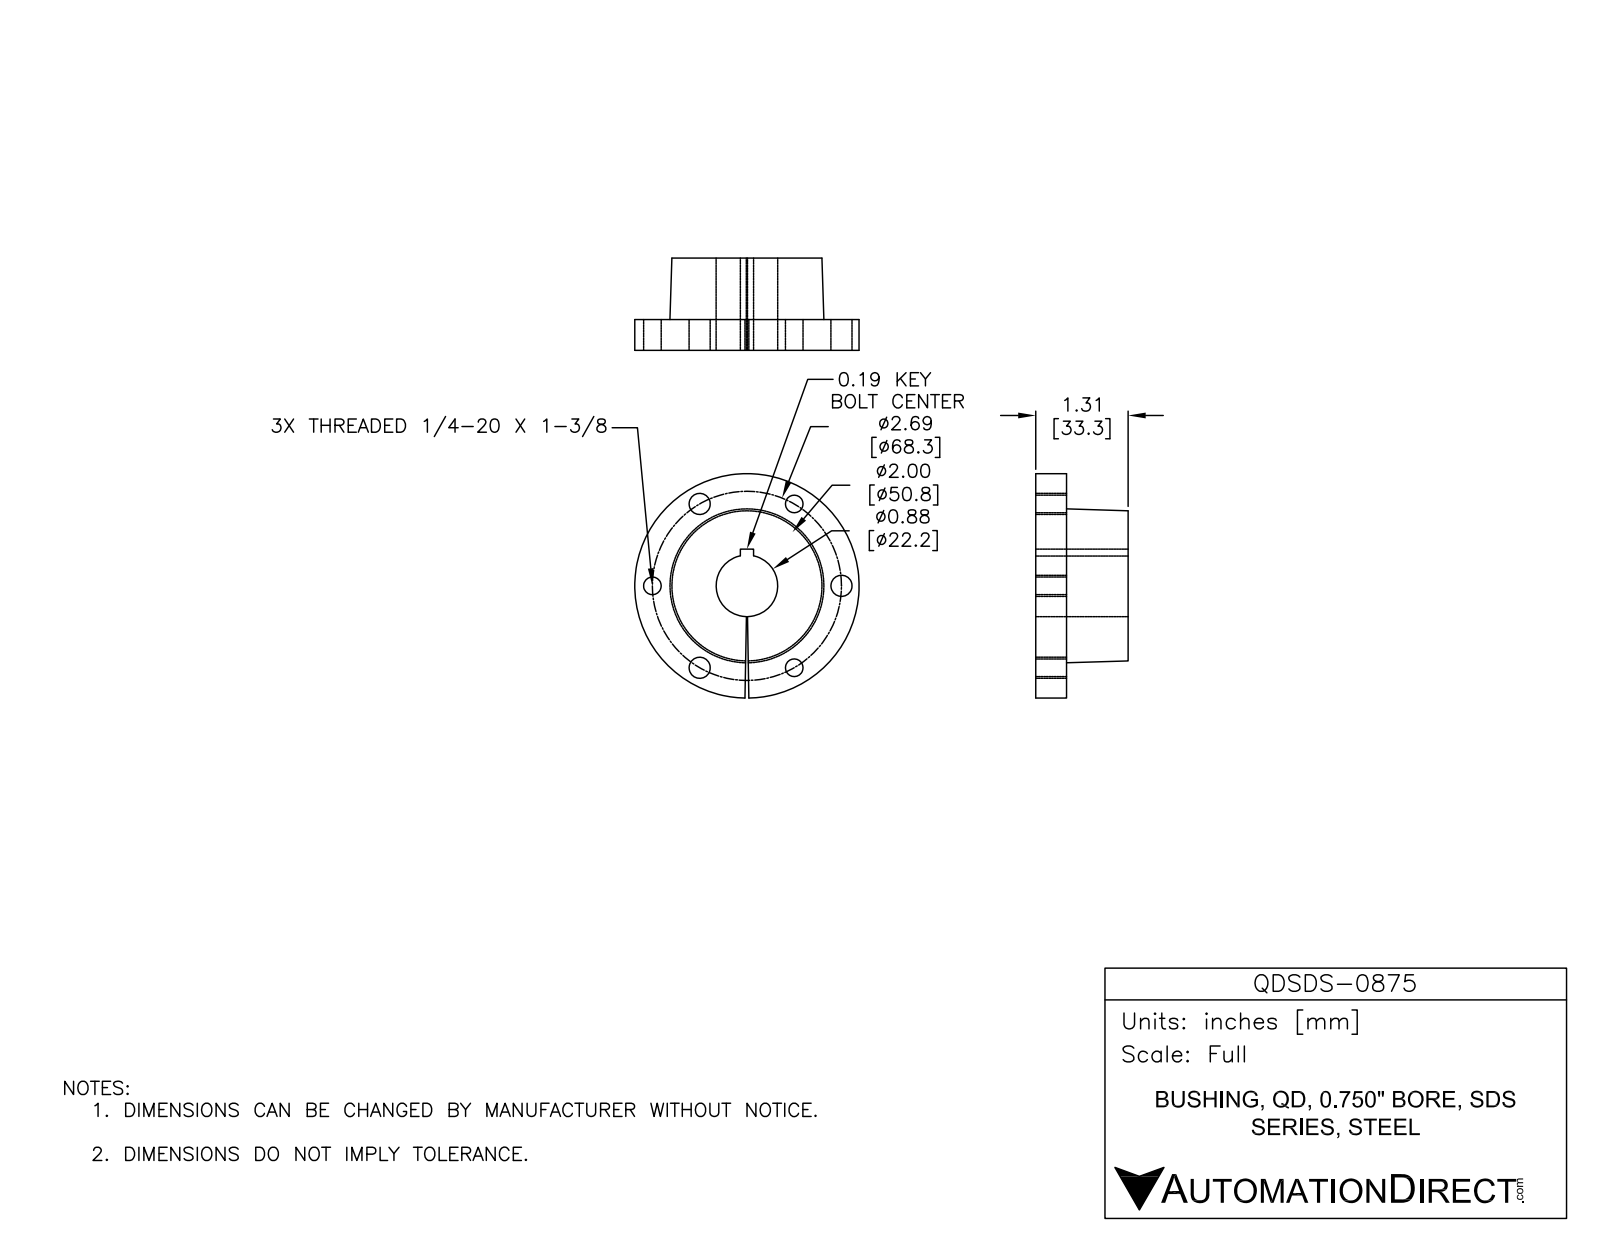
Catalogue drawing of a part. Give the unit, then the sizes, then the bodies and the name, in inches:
Units: inches
Overall size (bounding box): 3.188 × 3.187 × 1.313
Round holes (diameter × count): ⌀0.25 ×3, ⌀0.3 ×3, ⌀0.875 ×1
Round bosses / shafts (diameter × count): ⌀3.187 ×1
Main face-to-face distances: 0.437, 1.313, 0.875, 0.187
Hole centre spacings: 1.344, 2.328, 1.344, 2.688, 2.687
Volume: 5.695 in³ · Surface area: 32.26 in²
Bodies: 1 solid, 29 faces (8 planar, 18 cylindrical, 3 other)
Part name (STEP PRODUCT): QD-SDS-0875
STEP written by: SolidWorks 2014 (AUTOMOTIVE_DESIGN)
